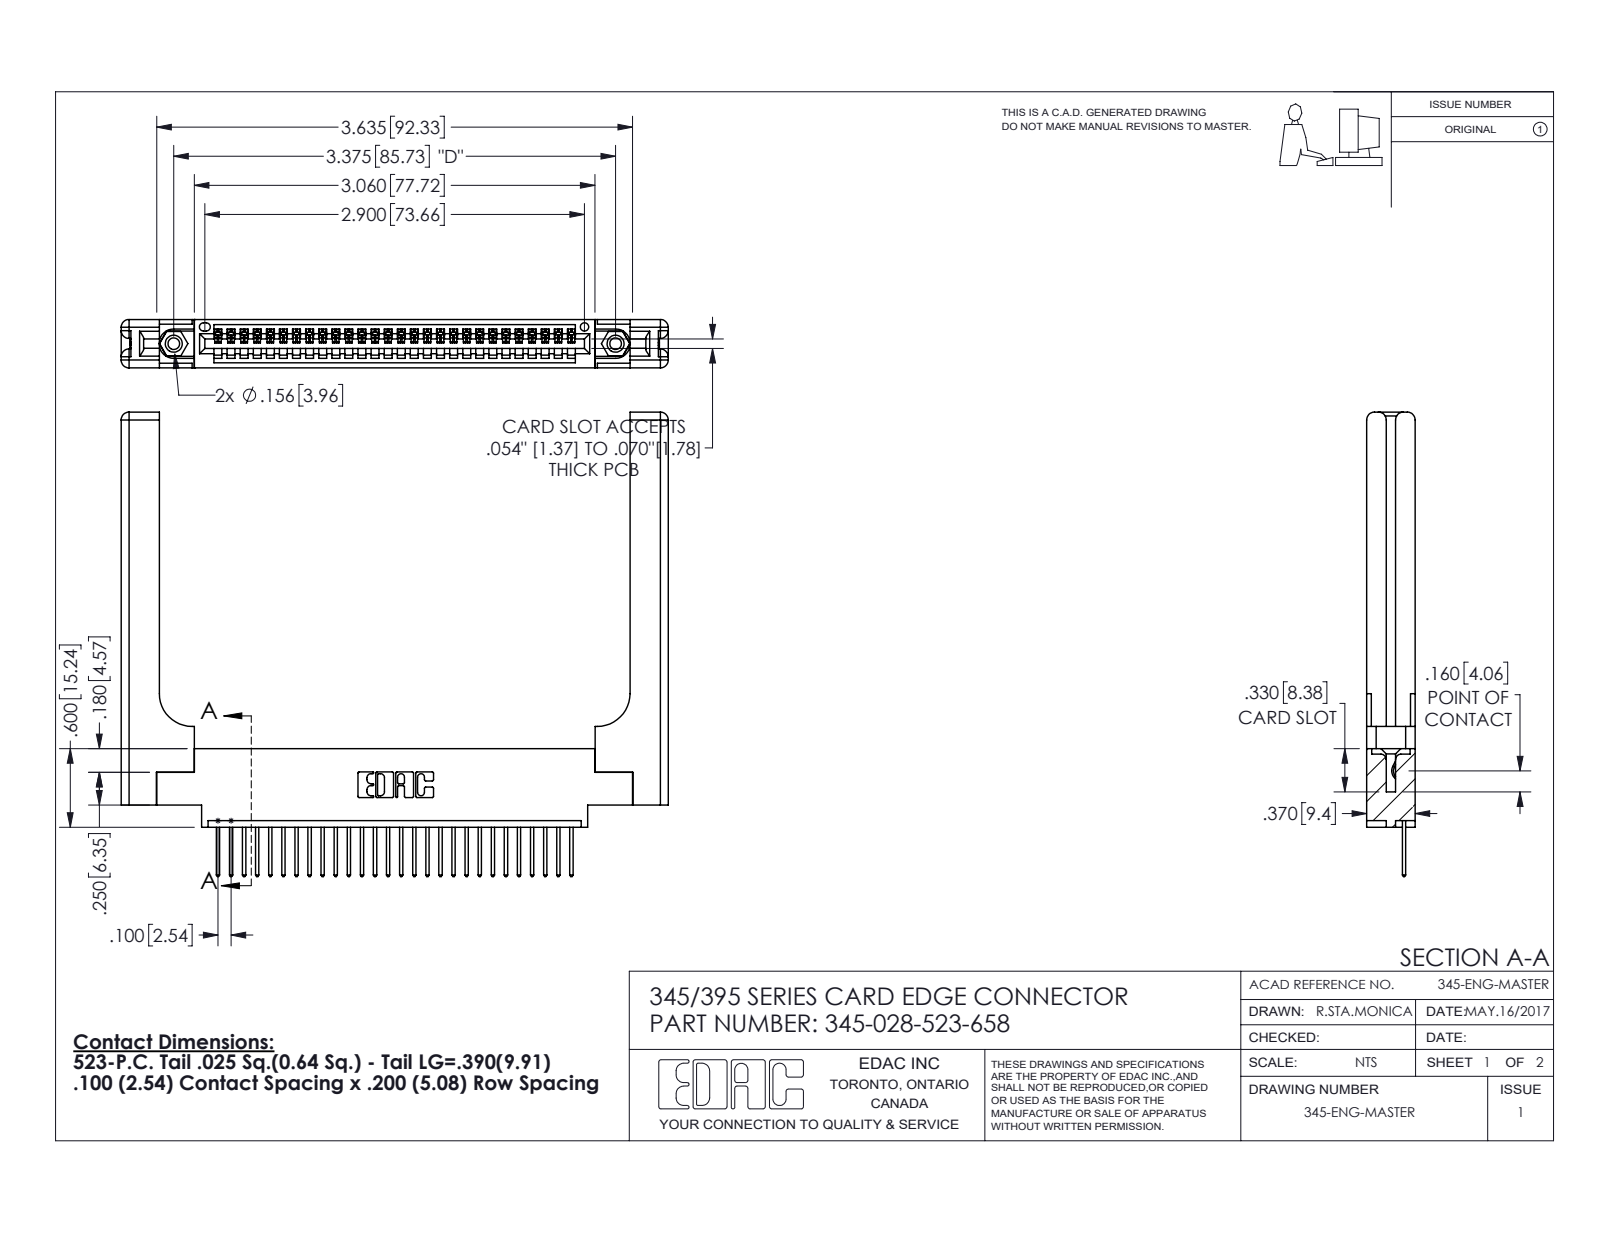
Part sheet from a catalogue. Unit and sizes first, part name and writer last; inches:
Units: inches
Overall size (bounding box): 4.179 × 3.547 × 0.37
Round holes (diameter × count): ⌀0.089 ×2, ⌀0.125 ×2, ⌀0.156 ×2, ⌀0.064 ×1
Round bosses / shafts (diameter × count): ⌀0.155 ×2
Partial cylindrical surfaces — rounded edges, fillets, slot ends (radius × count): R0.006 ×56, R0.01 ×56, R0.01 ×22, R0.06 ×16, R0.007 ×6, R0.031 ×6, R0.026 ×3, R0.03 ×2
Main face-to-face distances: 0.37, 0.072, 0.298, 0.098, 0.272, 0.025, 0.2, 0.148, 0.15, 0.077
Hole centre spacings: 0.27, 3.14, 3.375
Volume: 1.12 in³ · Surface area: 28.45 in²
Bodies: 33 solids, 2010 faces (1352 planar, 598 cylindrical, 60 other)
Part name (STEP PRODUCT): 345-028-523-658; 345 Part_0.170 Offset - 0.156 Dia-TH; 345-250-001_345-250-001-102; 345-220-058_345-220-058 (+1 more)
STEP written by: SolidWorks 2016 (CONFIG_CONTROL_DESIGN)
